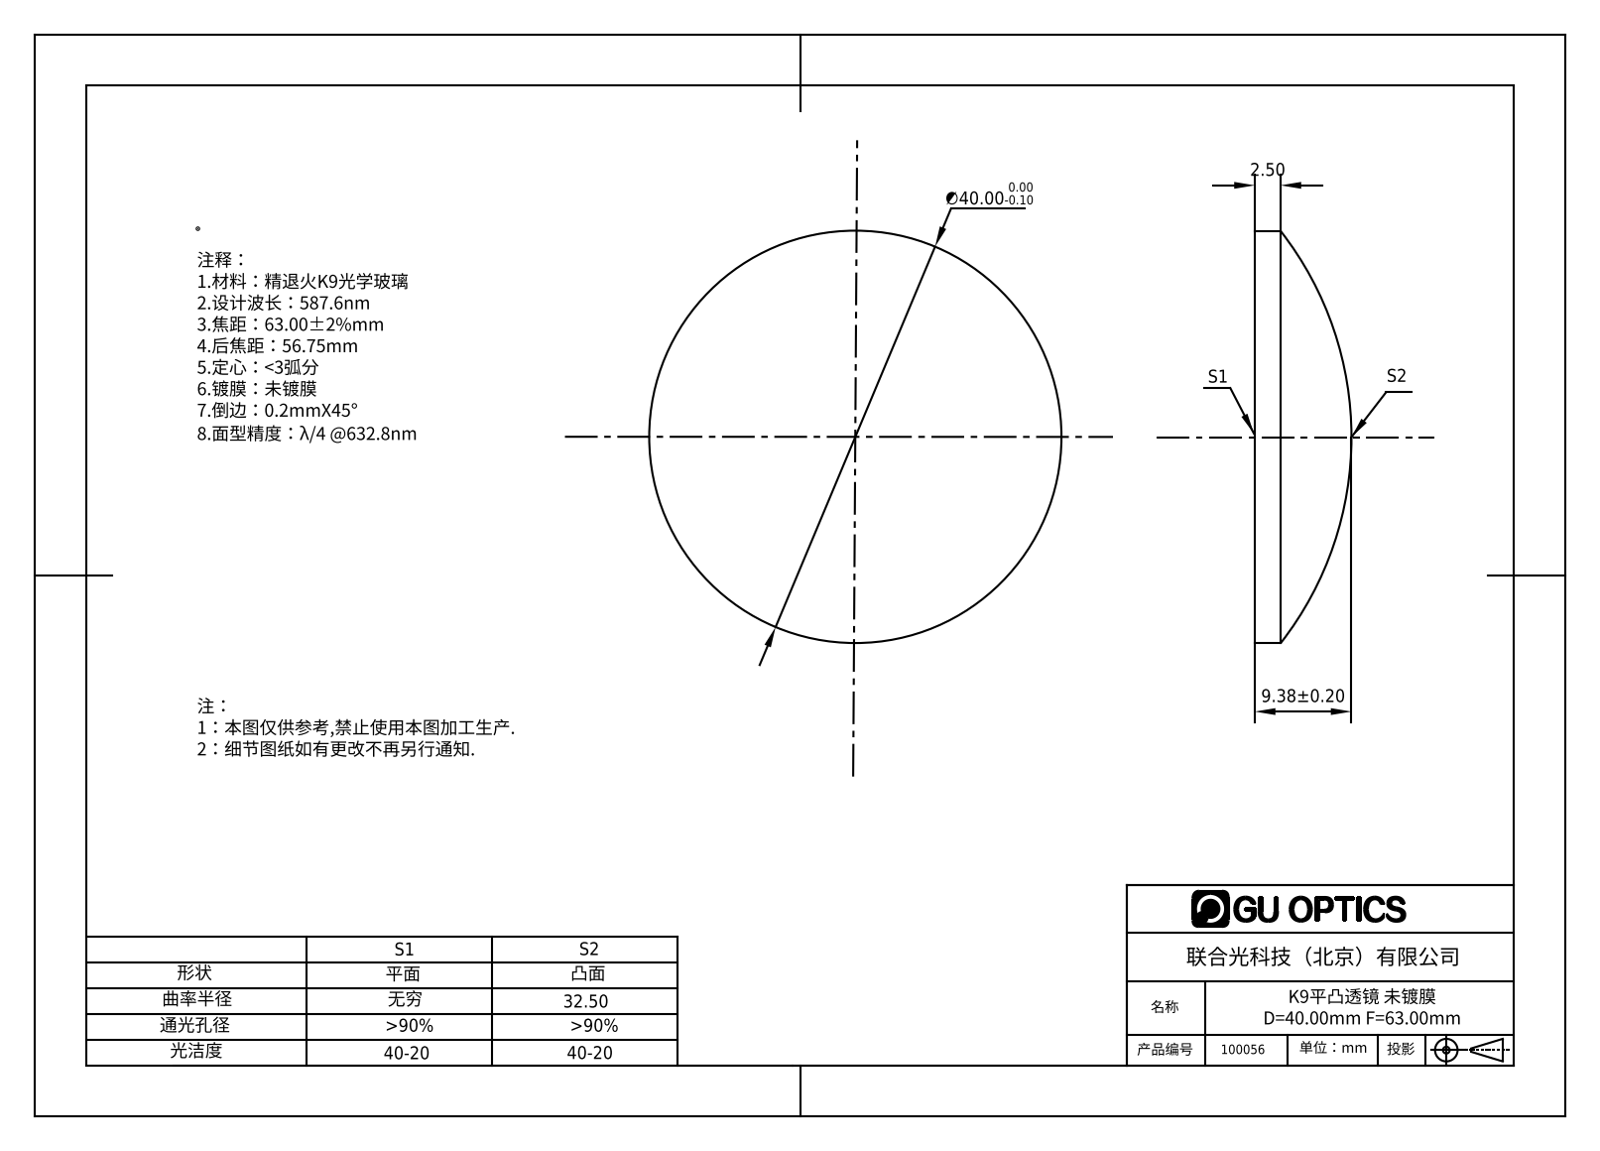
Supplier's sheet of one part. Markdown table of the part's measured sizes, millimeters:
| quantity | value |
| --- | --- |
| part name | 100056 |
| STEP written by | SolidWorks 2016 (AUTOMOTIVE_DESIGN) |
| units | millimeters |
| bodies | 1 solid, 5 faces (1 planar, 2 cylindrical, 2 other) |
| overall size | 40 × 40 × 9.38 |
| volume | 7 635 mm³ |
| surface area | 2 976 mm² |
| round bosses / shafts (diameter × count) | 40 × 1 |
